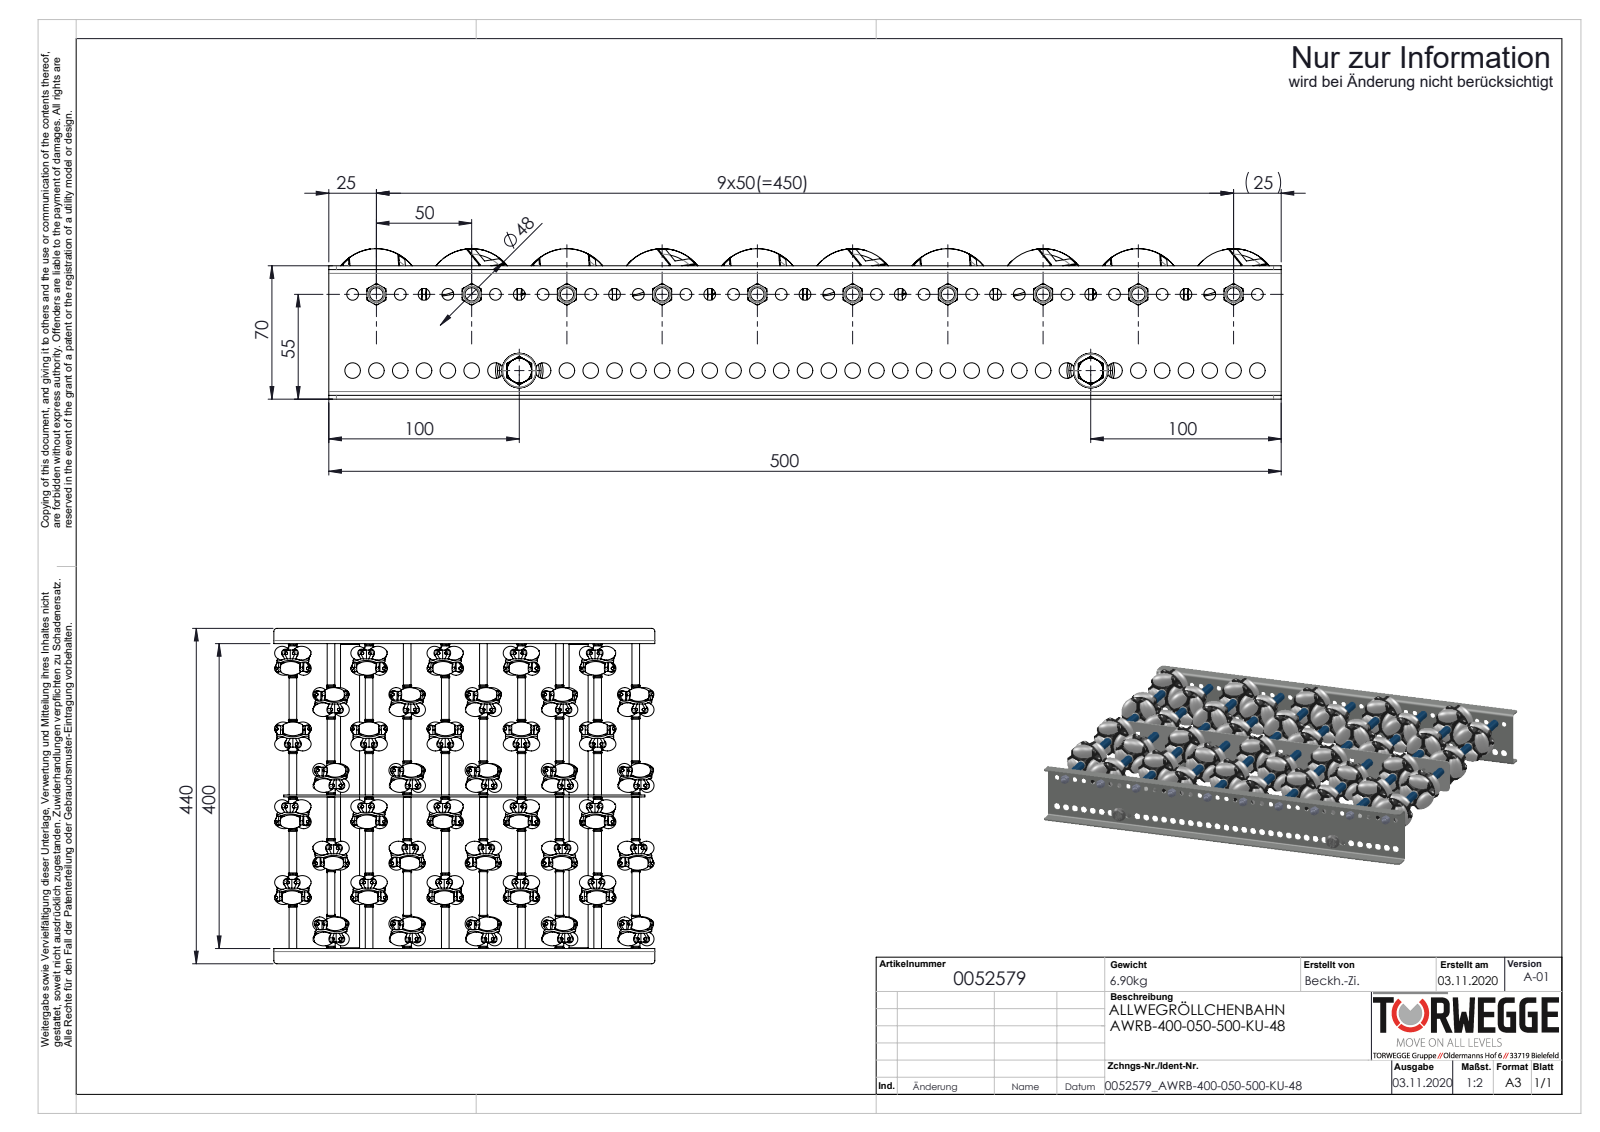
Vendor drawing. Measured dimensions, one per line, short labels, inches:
name: 0015028_AWR48; AWR-Achse-für-Konfiguration_L400; AWR48_Röllchen; S108767_Längstraverse-42x2,5-AWR_L500 (+8 more)
written by: SolidWorks 2020 (AUTOMOTIVE_DESIGN)
unit: in
bodies: 683 solids, 12180 faces (4226 planar, 4670 cylindrical, 3284 other)
size: 19.685 × 17.323 × 3.11
volume: 141 in³; area: 2 461 in²
holes: 240× ⌀0.146, 240× ⌀0.165, 39× ⌀0.244, 39× ⌀0.323, 19× ⌀0.256, 10× ⌀0.194, 10× ⌀0.331, 2× ⌀0.268, 2× ⌀0.827
bosses: 240× ⌀0.157, 189× ⌀0.146, 12× ⌀0.315, 10× ⌀1.654, 10× ⌀0.433, 10× ⌀0.394, 10× ⌀0.276, 10× ⌀0.236
rounds: 10× R0.927, 8× R0.157, 4× R0.079, 4× R0.197
face distances: 0.079, 15.827, 2.677, 15.748, 15.906, 0.118, 7.898, 7.819, 7.929, 8.008
hole spacings: 1.42, 1.419, 1.419, 0.492, 3.445, 2.988, 0.724, 0.984
